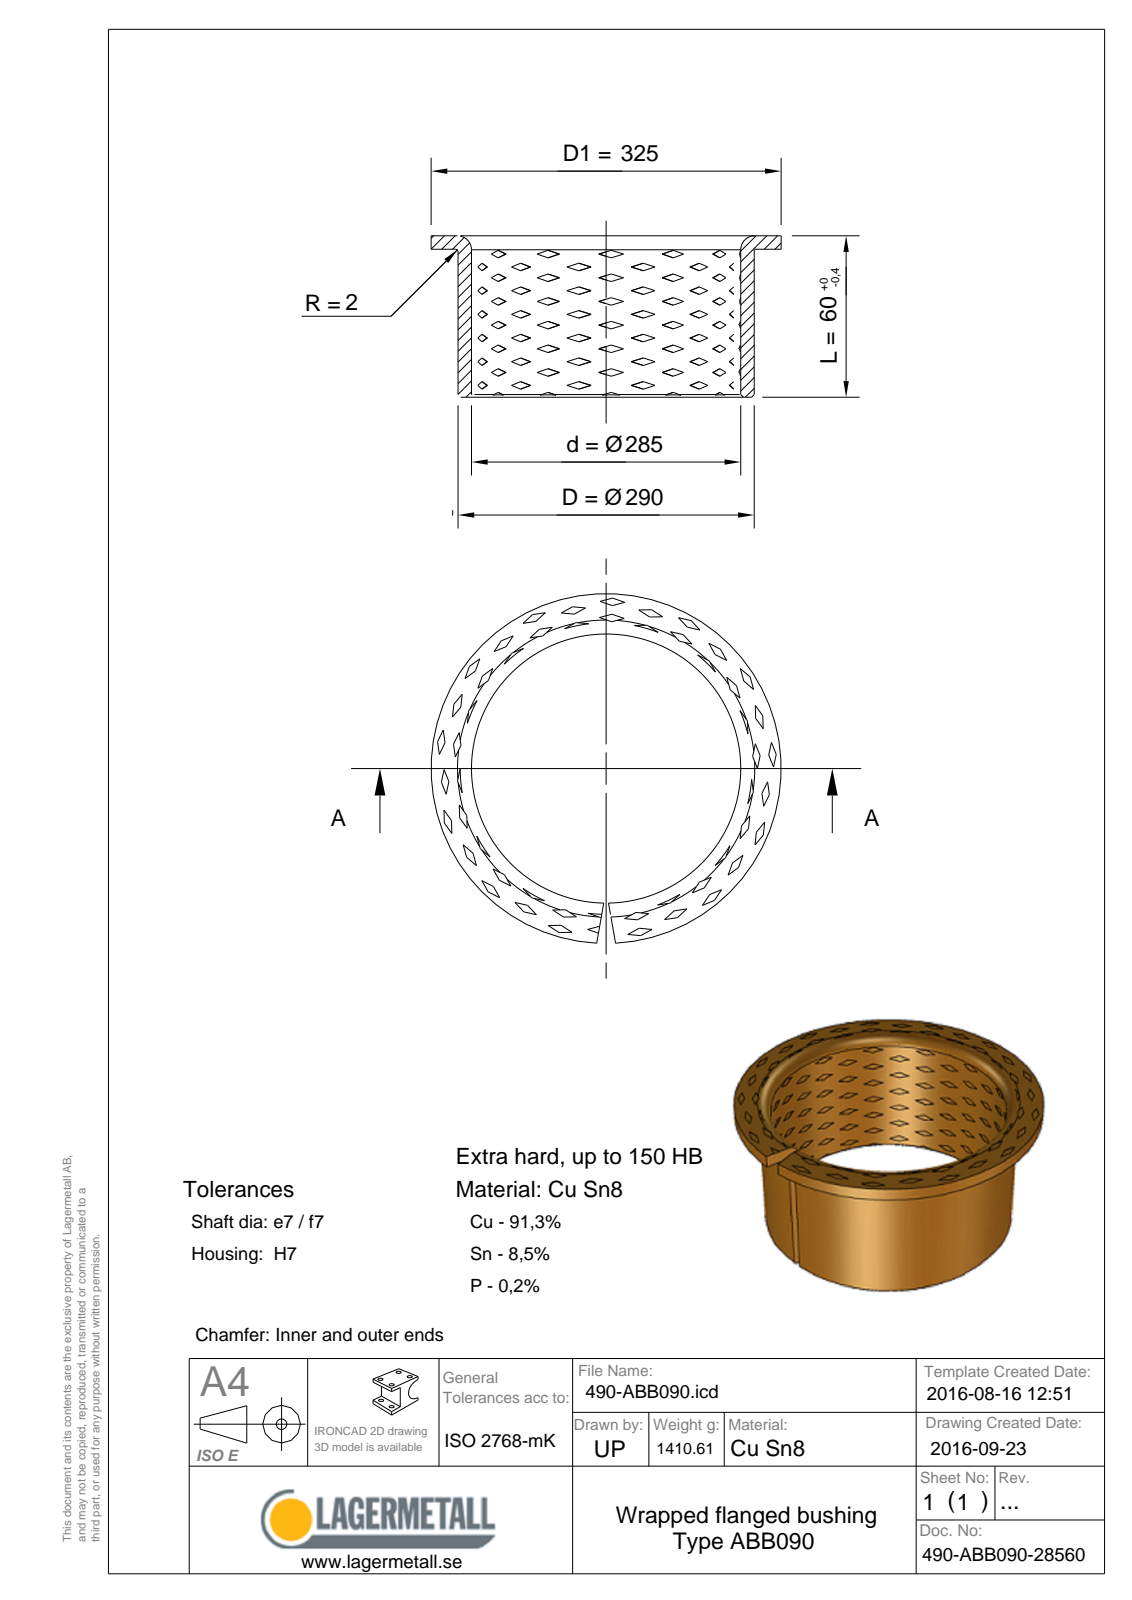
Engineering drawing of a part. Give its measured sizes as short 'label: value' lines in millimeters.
written by: Spatial InterOp 3D (CONFIG_CONTROL_DESIGN)
unit: mm
bodies: 1 solid, 26 faces (5 planar, 9 cylindrical, 12 other)
size: 325 × 325 × 60
volume: 174 147 mm³; area: 144 134 mm²
holes: 1× ⌀285
bosses: 1× ⌀325, 1× ⌀290
face distances: 2.5, 57.5, 60
